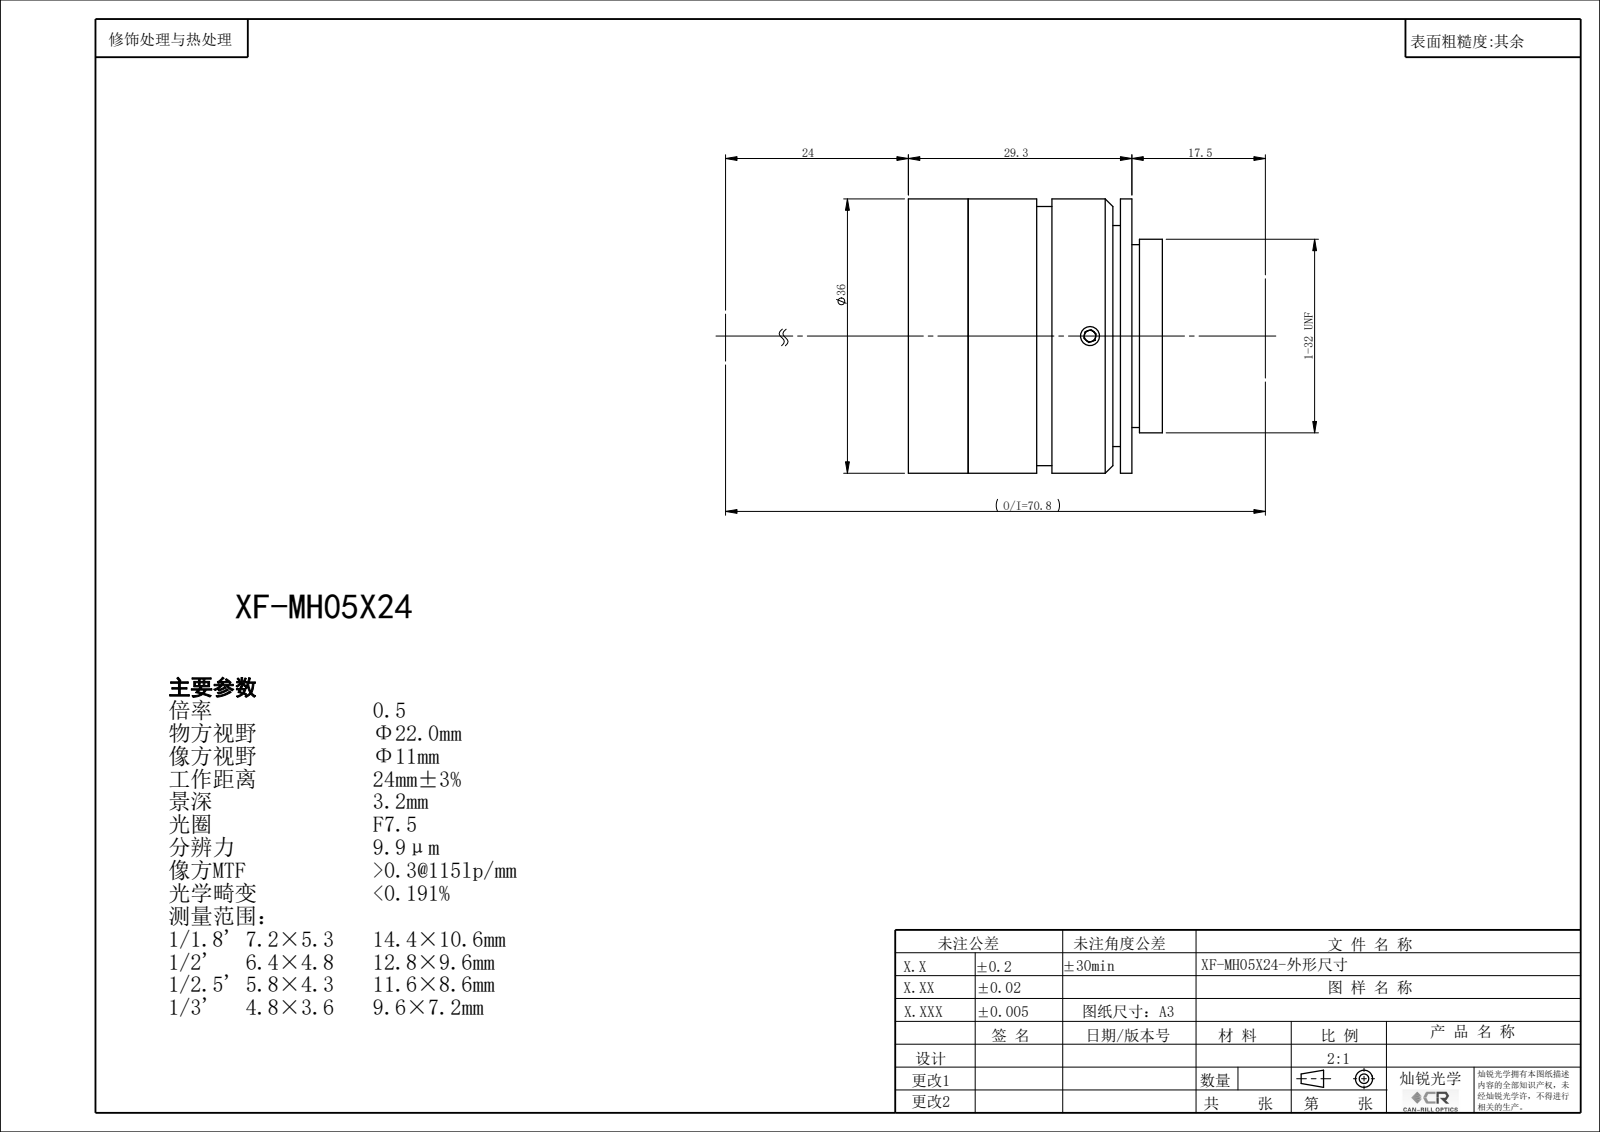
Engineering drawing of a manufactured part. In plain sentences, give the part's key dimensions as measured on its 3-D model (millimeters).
The part is named "XF-MH05X24". Its 3-D file was written by "SolidWorks 2022 (CONFIG_CONTROL_DESIGN)". It is 0 solids with 108 faces: 52 planar, 46 cylindrical and 10 other. Overall it measures 36 by 36 by 33.34 millimeters. Round holes: 3 of diameter 2.5, 1 of diameter 7, 1 of diameter 8.4, 1 of diameter 10, 1 of diameter 12, 1 of diameter 14, 1 of diameter 16, 1 of diameter 18, 1 of diameter 20, 1 of diameter 21.5, 1 of diameter 22, 1 of diameter 24. Round bosses or shafts: 1 of diameter 36, 1 of diameter 34, 1 of diameter 25.4. The main face-to-face distances are 7.85, 21.49, 29.34, 2, 1, 1.5, 27.84, 19.99, 4, 26.85.
